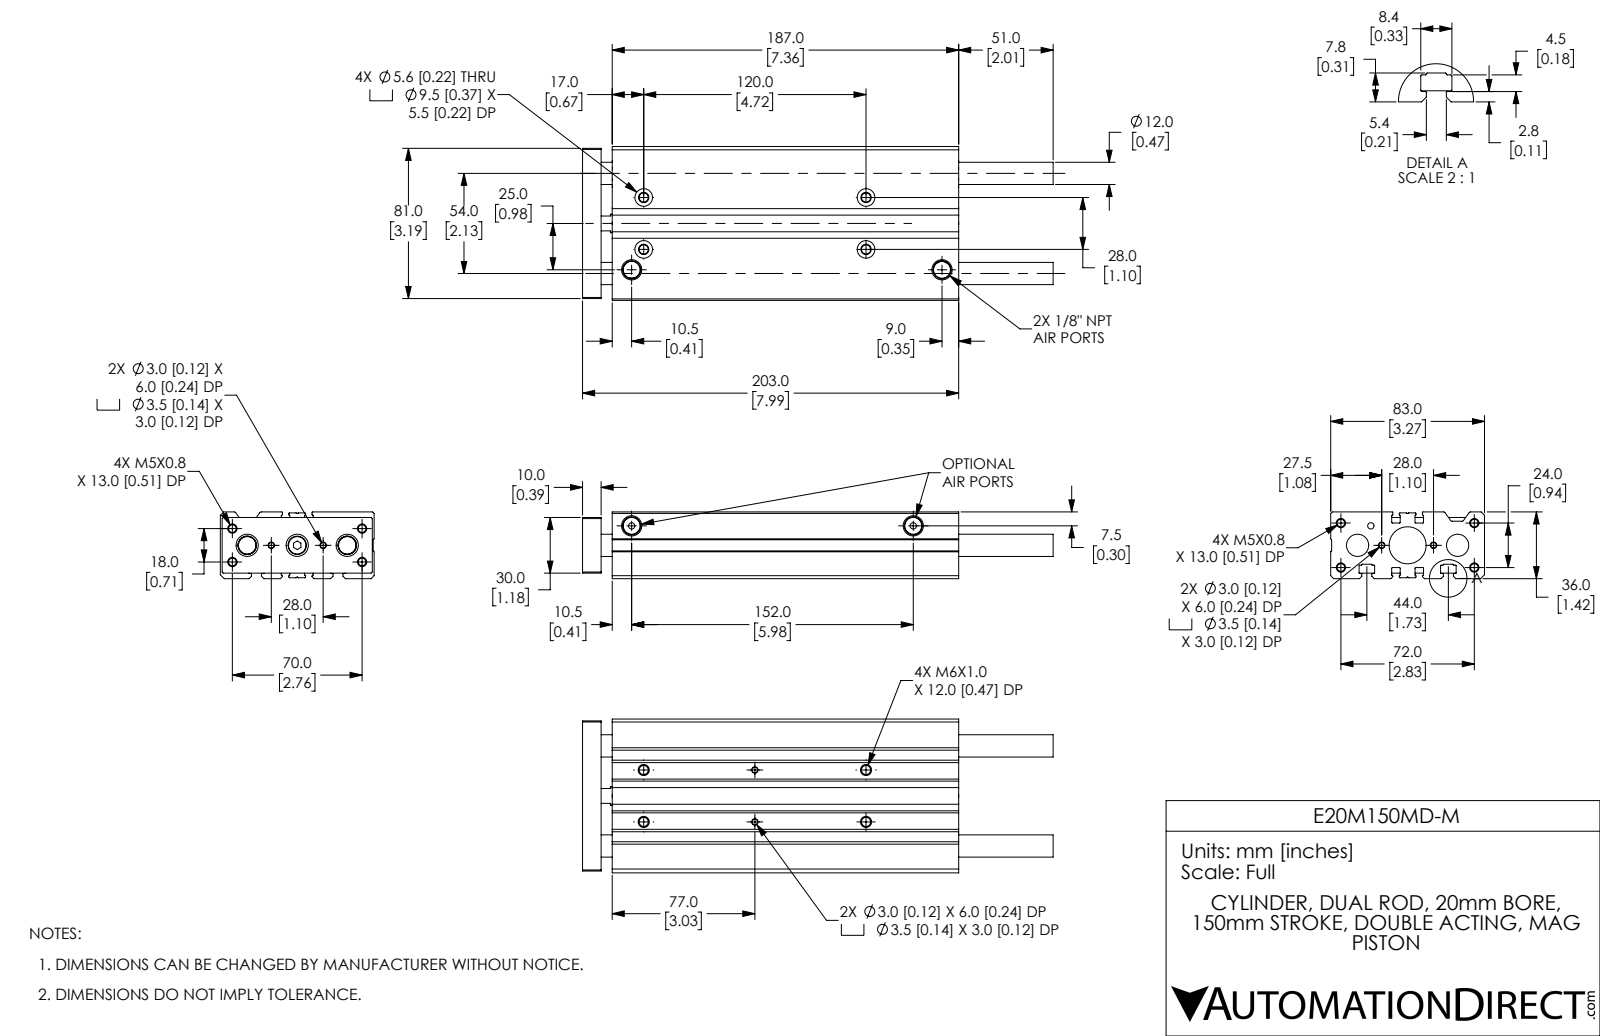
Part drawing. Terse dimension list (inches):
name: E20M150MD-M_BODY; E20M150MD-M; E20M150MD-M_ENDPLATE
written by: SolidWorks 2019 (CONFIG_CONTROL_DESIGN)
unit: in
bodies: 5 solids, 405 faces (128 planar, 182 cylindrical, 95 other)
size: 10 × 3.268 × 1.417
volume: 30.36 in³; area: 205.7 in²
holes: 8× ⌀0.163, 4× ⌀0.118, 4× ⌀0.138, 4× ⌀0.194, 4× ⌀0.22, 4× ⌀0.374, 3× ⌀0.236, 3× ⌀0.472, 2× ⌀0.135, 2× ⌀0.39, 1× ⌀0.135, 1× ⌀0.472
bosses: 1× ⌀0.394, 1× ⌀0.39
rounds: 20× R0.016, 18× R0.008, 10× R0.012, 8× R0.01, 4× R0.039
face distances: 1.417, 0.02, 0.236, 3.268, 1.181, 0.118, 0.874, 1.791, 1.11, 1.476
hole spacings: 0.124, 0.474, 0.591, 0.828, 0.9, 0.987, 1.102, 1.423
